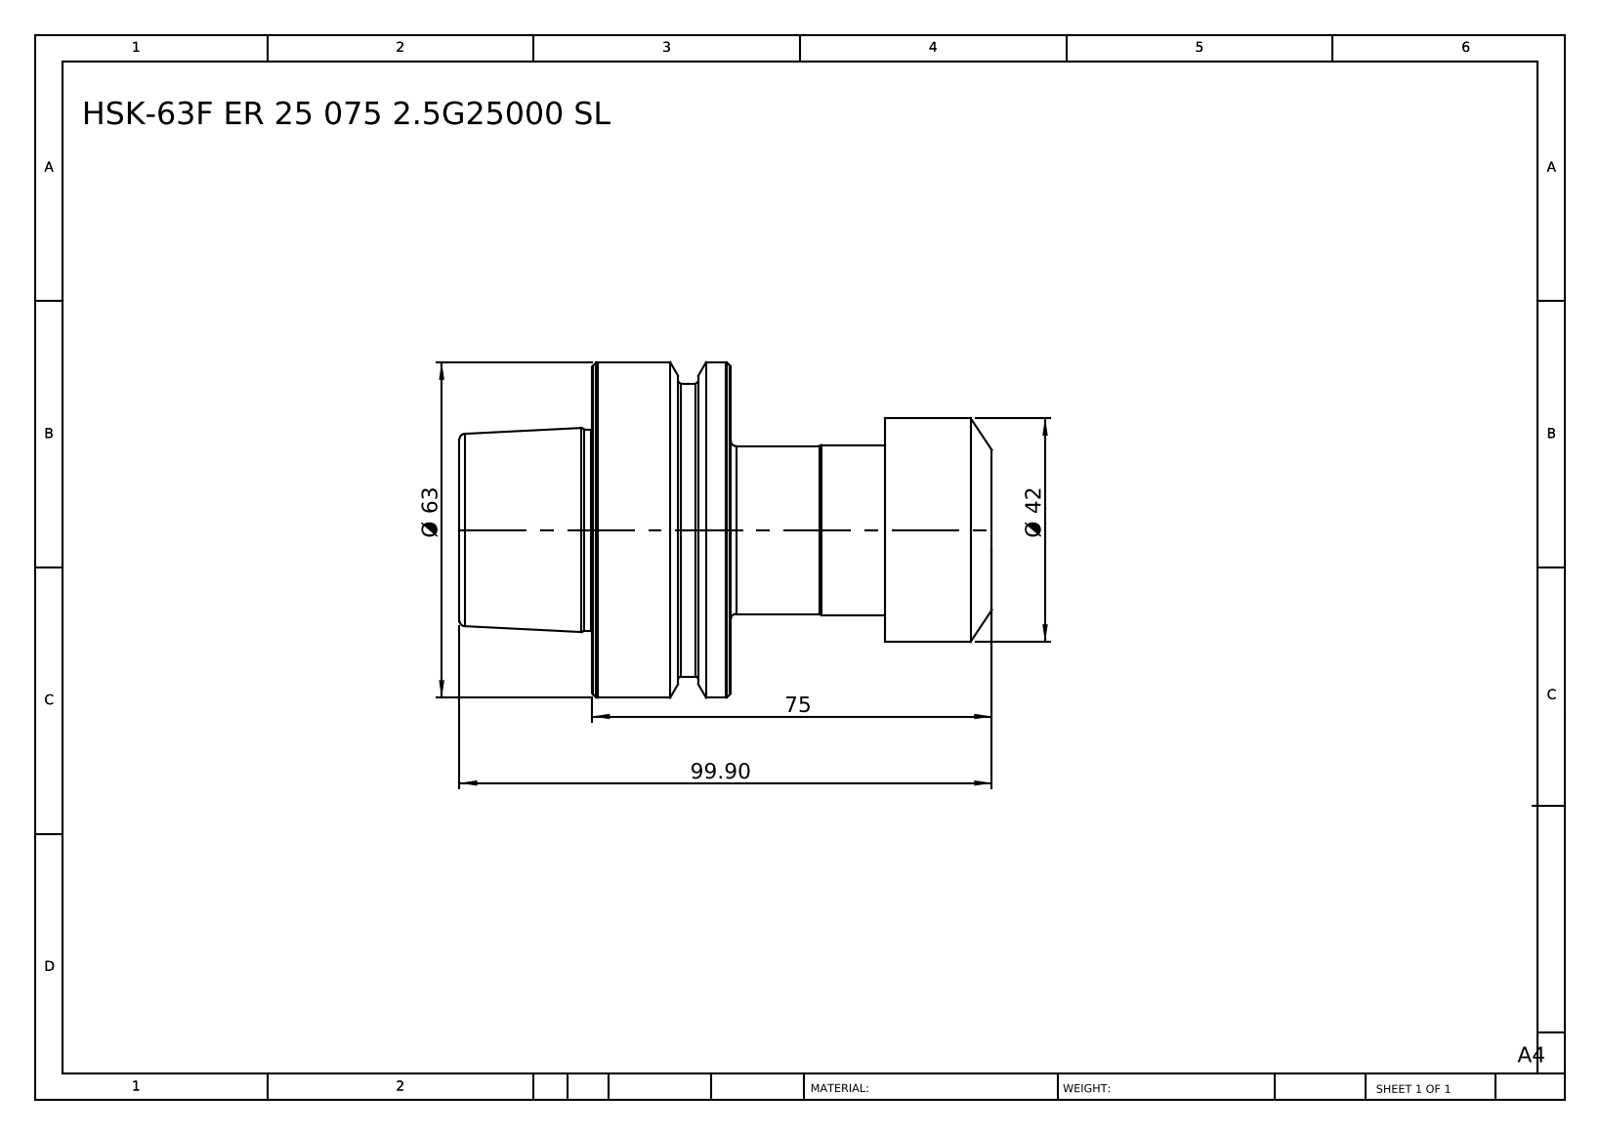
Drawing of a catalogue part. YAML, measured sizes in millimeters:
part_name: "HSK-63F ER 25 075 2.5G25000 SL"
step_written_by: "SolidWorks 2014 (CONFIG_CONTROL_DESIGN)"
units: millimeters
bodies: {solids: 1, faces: 57, planar: 7, cylindrical: 14, other: 36}
overall_size: [99.9, 63, 63]
volume: 153591
surface_area: 21119
round_bosses_or_shafts:
  - {diameter: 63, count: 1}
  - {diameter: 55, count: 1}
  - {diameter: 42, count: 1}
  - {diameter: 37.8, count: 1}
  - {diameter: 31.9, count: 1}
  - {diameter: 31.5, count: 1}
face_to_face_distances: [26, 50.9, 24.9, 49, 75, 99.9, 20, 29, 55, 79.9]
